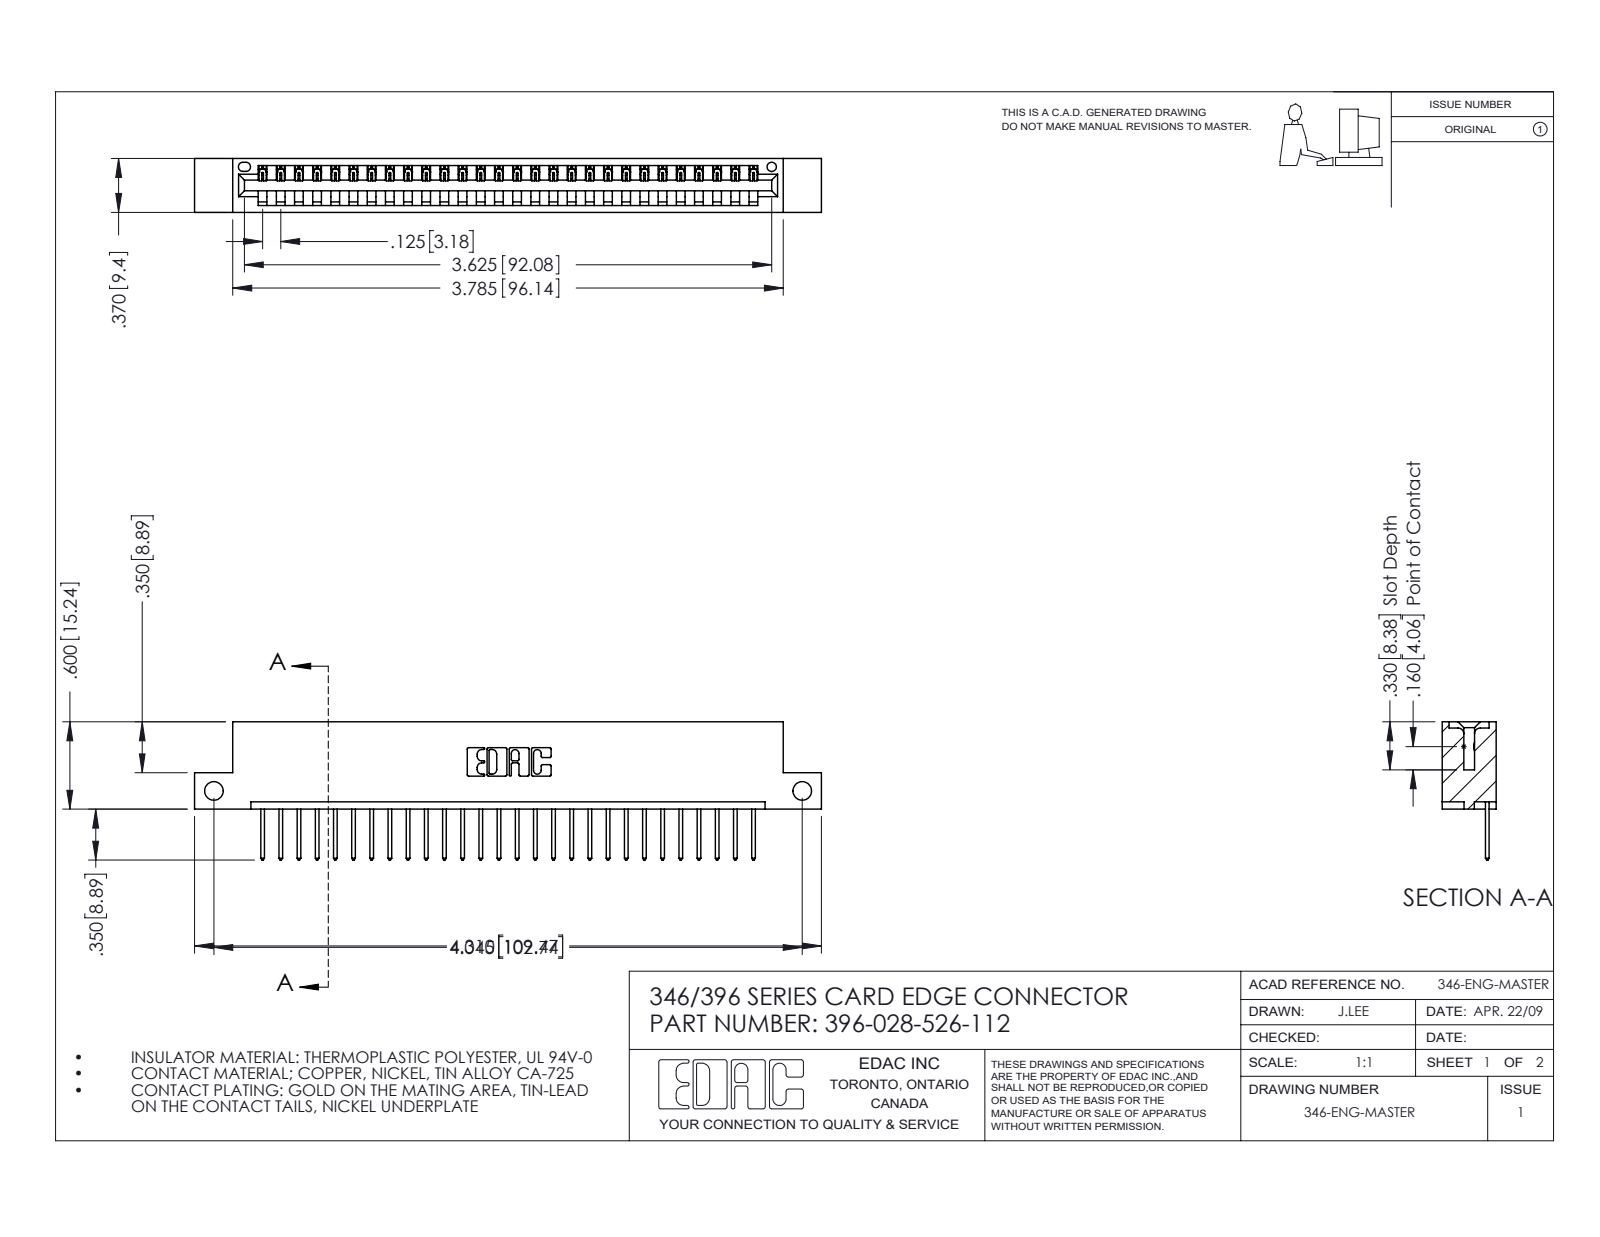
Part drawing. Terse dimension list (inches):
name: 346 Part_Flush Mounting Lugs - Side Mount; 345-292-001_345-293-126; 396-028-526-112
written by: SolidWorks 2016 (CONFIG_CONTROL_DESIGN)
unit: in
bodies: 29 solids, 1746 faces (1196 planar, 550 cylindrical, 0 other)
size: 4.31 × 0.95 × 0.37
volume: 0.627 in³; area: 19.4 in²
holes: 2× ⌀0.128, 1× ⌀0.064
rounds: 56× R0.006, 56× R0.01, 22× R0.01, 6× R0.007, 6× R0.031, 3× R0.026, 2× R0.031, 2× R0.04
face distances: 0.048, 0.322, 0.37, 0.25, 0.072, 0.298, 0.025, 0.148, 0.222, 0.1
hole spacings: 4.045
